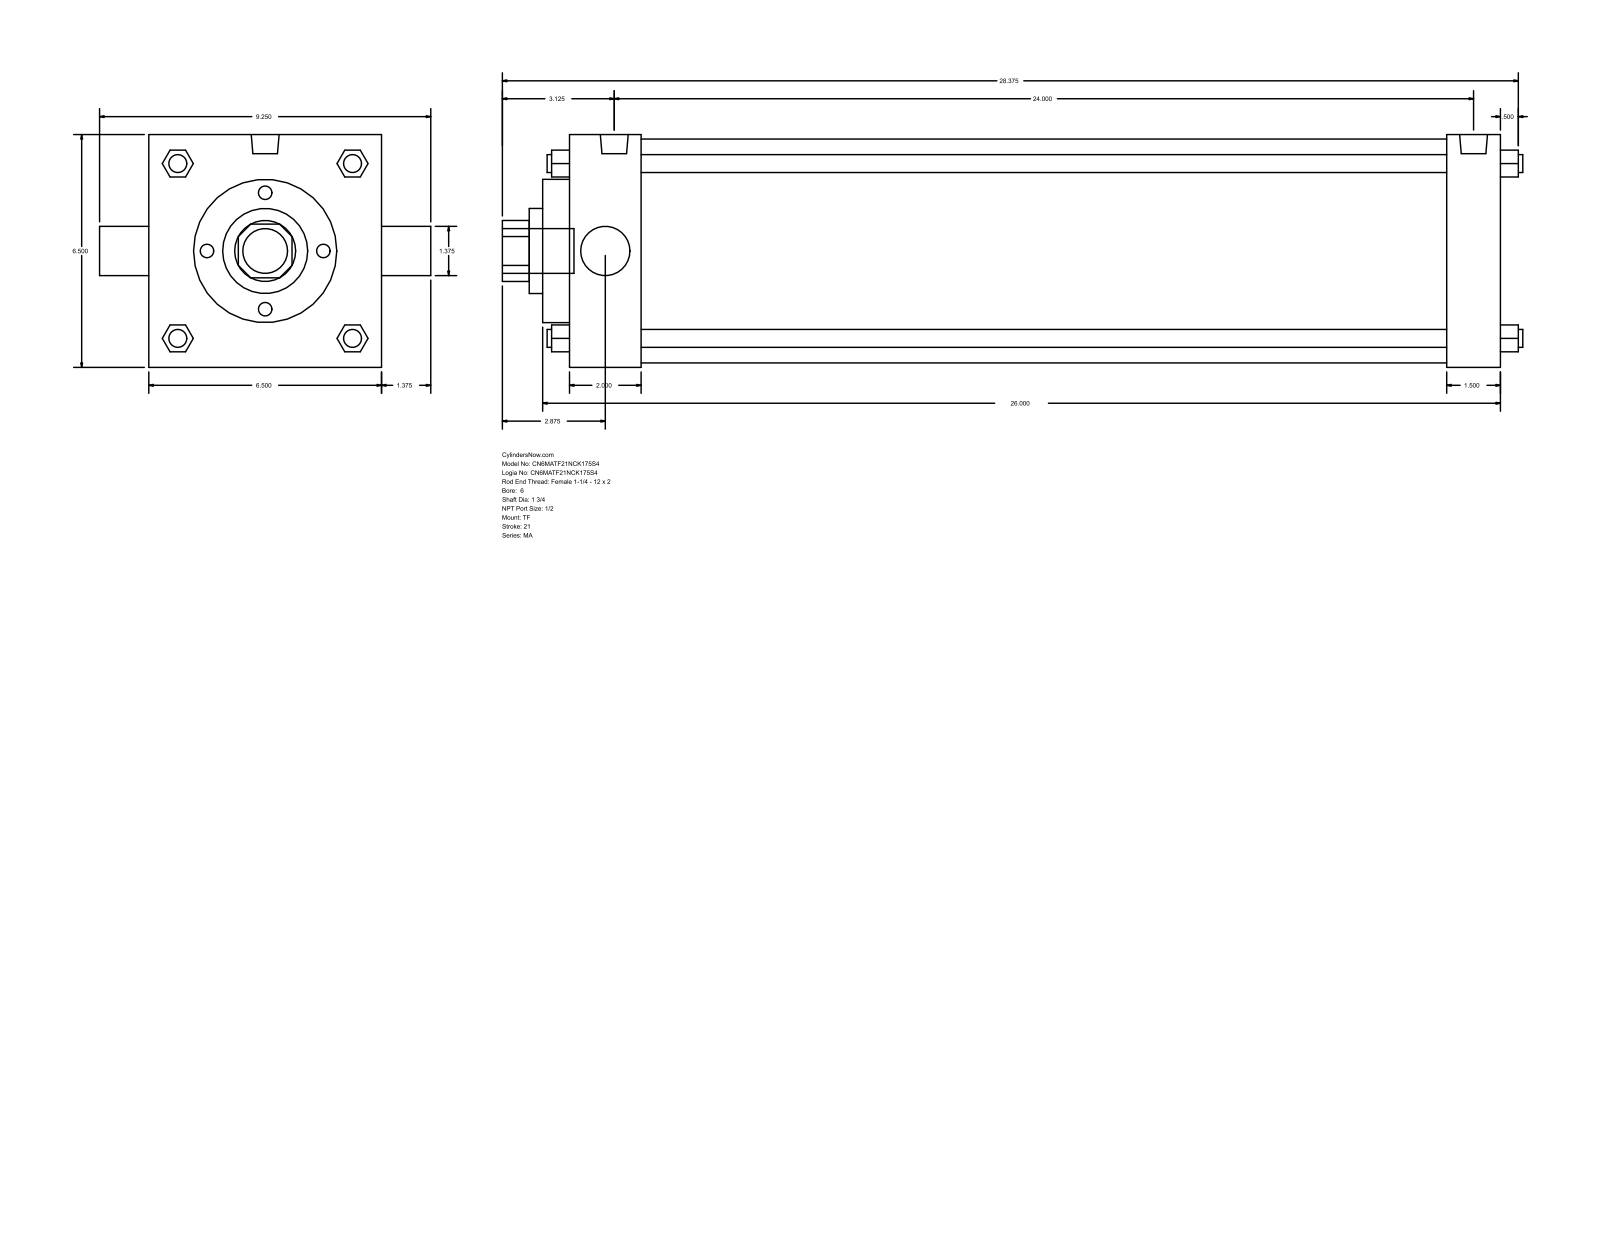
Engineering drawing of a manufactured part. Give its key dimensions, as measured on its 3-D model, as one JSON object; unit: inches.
{"part_name": "MA_TF__0600_1.75", "step_written_by": "GSSL Pune (CONFIG_CONTROL_DESIGN)", "units": "inches", "bodies": {"solids": 0, "faces": 122, "planar": 93, "cylindrical": 29, "other": 0}, "overall_size": [28.5, 9.25, 6.5], "round_holes": [[1.375, 1], [1.75, 1], [2.375, 1], [4, 1], [6.25, 1]], "round_bosses_or_shafts": [[0.5, 4], [0.687, 3], [0.778, 2], [1.25, 1]], "partial_cylinders_radius": [[0.852, 1]], "face_to_face_distances": [6.5, 26, 0.75, 1.5, 2, 24, 24.5, 22.5, 2.75, 25.25]}
